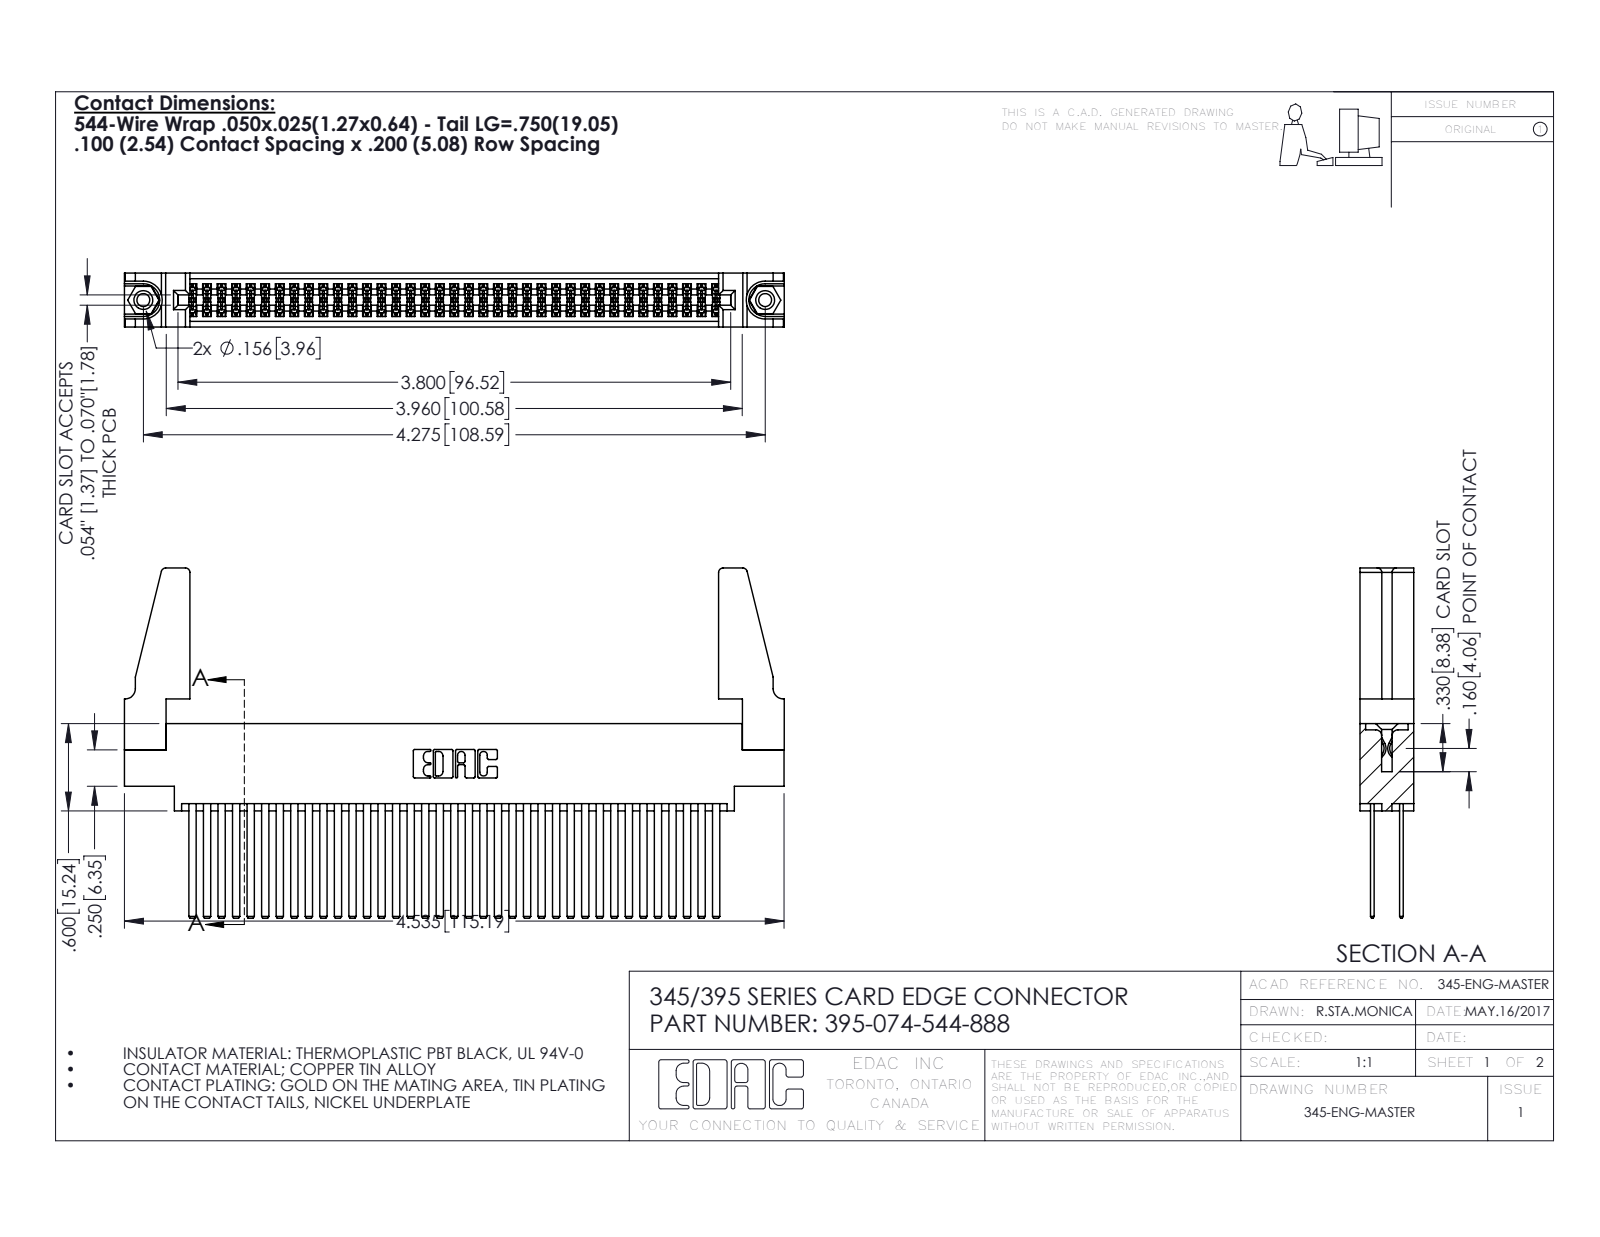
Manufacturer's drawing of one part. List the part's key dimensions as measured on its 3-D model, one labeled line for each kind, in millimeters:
Part name (STEP PRODUCT): 345-292-001_345-293-144; 395-074-544-888; 345-250-001_345-250-001-102; 345 Part_0.170 Offset - 0.156 Dia-TH (+1 more)
STEP written by: SolidWorks 2016 (CONFIG_CONTROL_DESIGN)
Units: millimetres
Bodies: 79 solids, 3510 faces (2302 planar, 1192 cylindrical, 16 other)
Overall size (bounding box): 115.2 × 61.1 × 9.4
Volume: 15 300 mm³ · Surface area: 24 050 mm²
Round holes (diameter × count): ⌀2.3 ×2, ⌀3.2 ×2, ⌀4 ×2, ⌀1.6 ×1
Round bosses / shafts (diameter × count): ⌀3.9 ×2
Partial cylindrical surfaces — rounded edges, fillets, slot ends (radius × count): R0.2 ×111, R0.3 ×22, R0.8 ×8, R0.2 ×6, R0.8 ×6, R0.7 ×3, R0.4 ×2, R0.5 ×2
Main face-to-face distances: 1.8, 7.6, 5.1, 2.5, 6.9, 0.6, 9.4, 5.7, 4.4, 3.8
Hole centre spacings: 6.9, 102.6, 108.6
